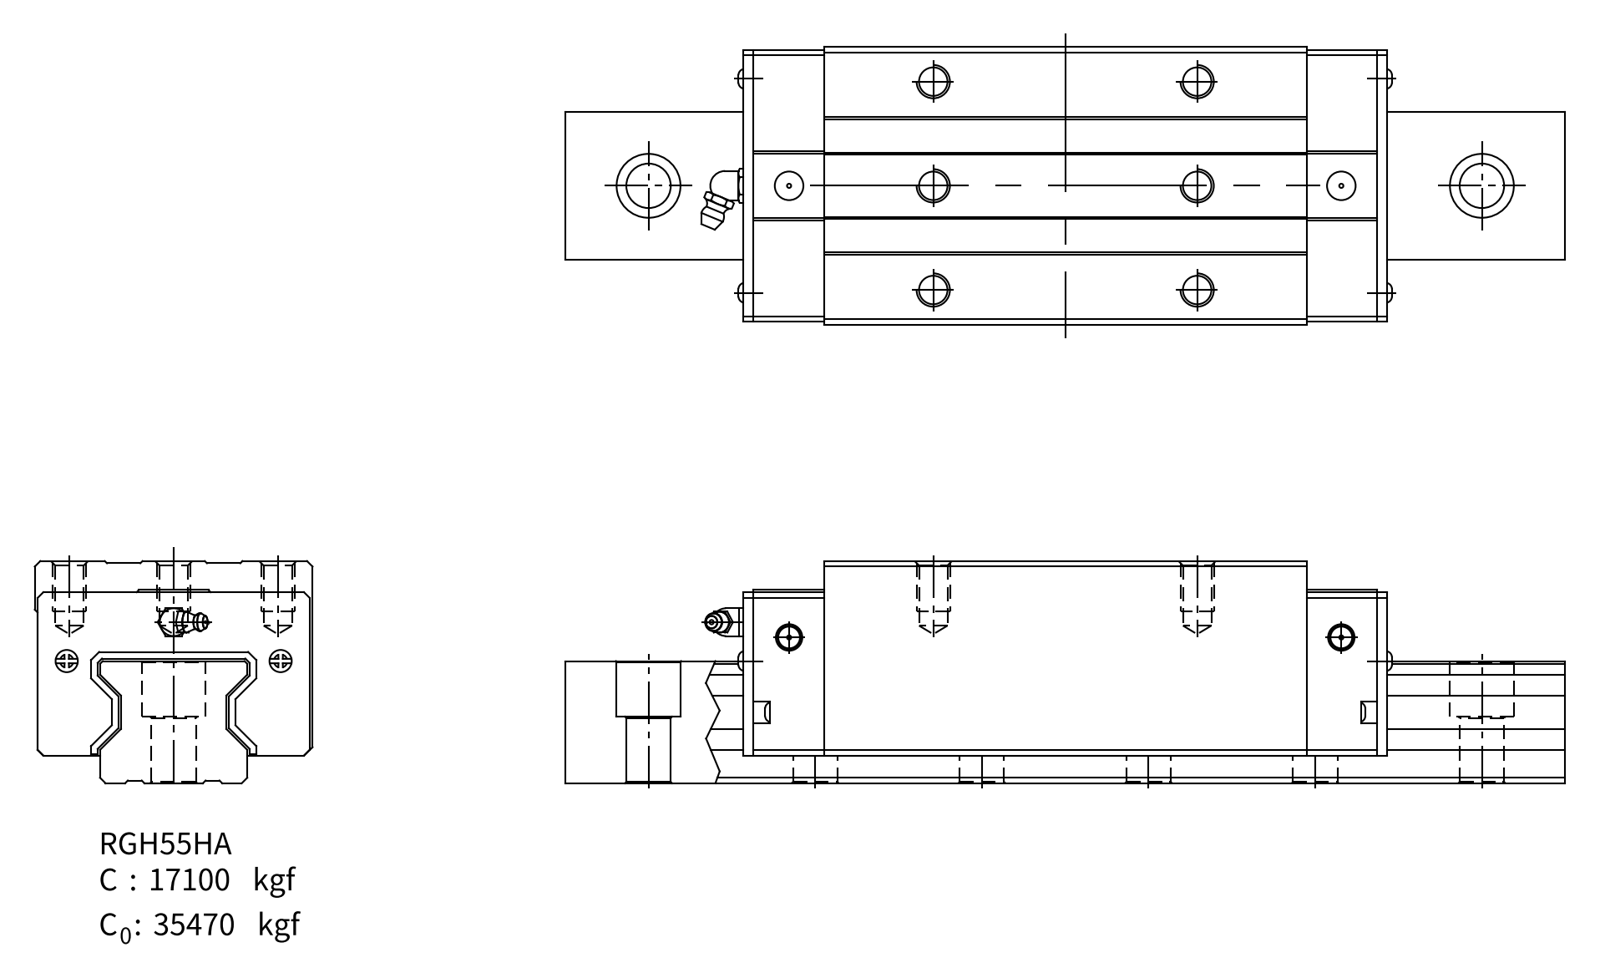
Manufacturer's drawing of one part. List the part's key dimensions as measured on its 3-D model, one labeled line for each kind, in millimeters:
Part name (STEP PRODUCT): RGH55HA_BLOCK_7; PRT0026; RGH55HA_ASM_5_ASM; RGH55HA_ASM
STEP written by: PRO/ENGINEER BY PARAMETRIC TECHNOLOGY CORPORATION, 2004360 (CONFIG_CONTROL_DESIGN)
Units: millimetres
Bodies: 2 solids, 181 faces (103 planar, 56 cylindrical, 22 other)
Overall size (bounding box): 300 × 100 × 80
Volume: 1 717 000 mm³ · Surface area: 188 213 mm²
Round holes (diameter × count): ⌀12 ×6, ⌀16 ×5, ⌀23 ×5, ⌀1.5 ×2, ⌀8.5 ×2, ⌀10.3 ×2, ⌀10 ×1, ⌀12.5 ×1
Main face-to-face distances: 99, 34, 21.03, 36, 22.5, 75.5, 76.5, 23.5, 10, 70
Hole centre spacings: 37.5, 39.53, 60, 60.52, 64.03, 81.62, 102.13, 113.85
